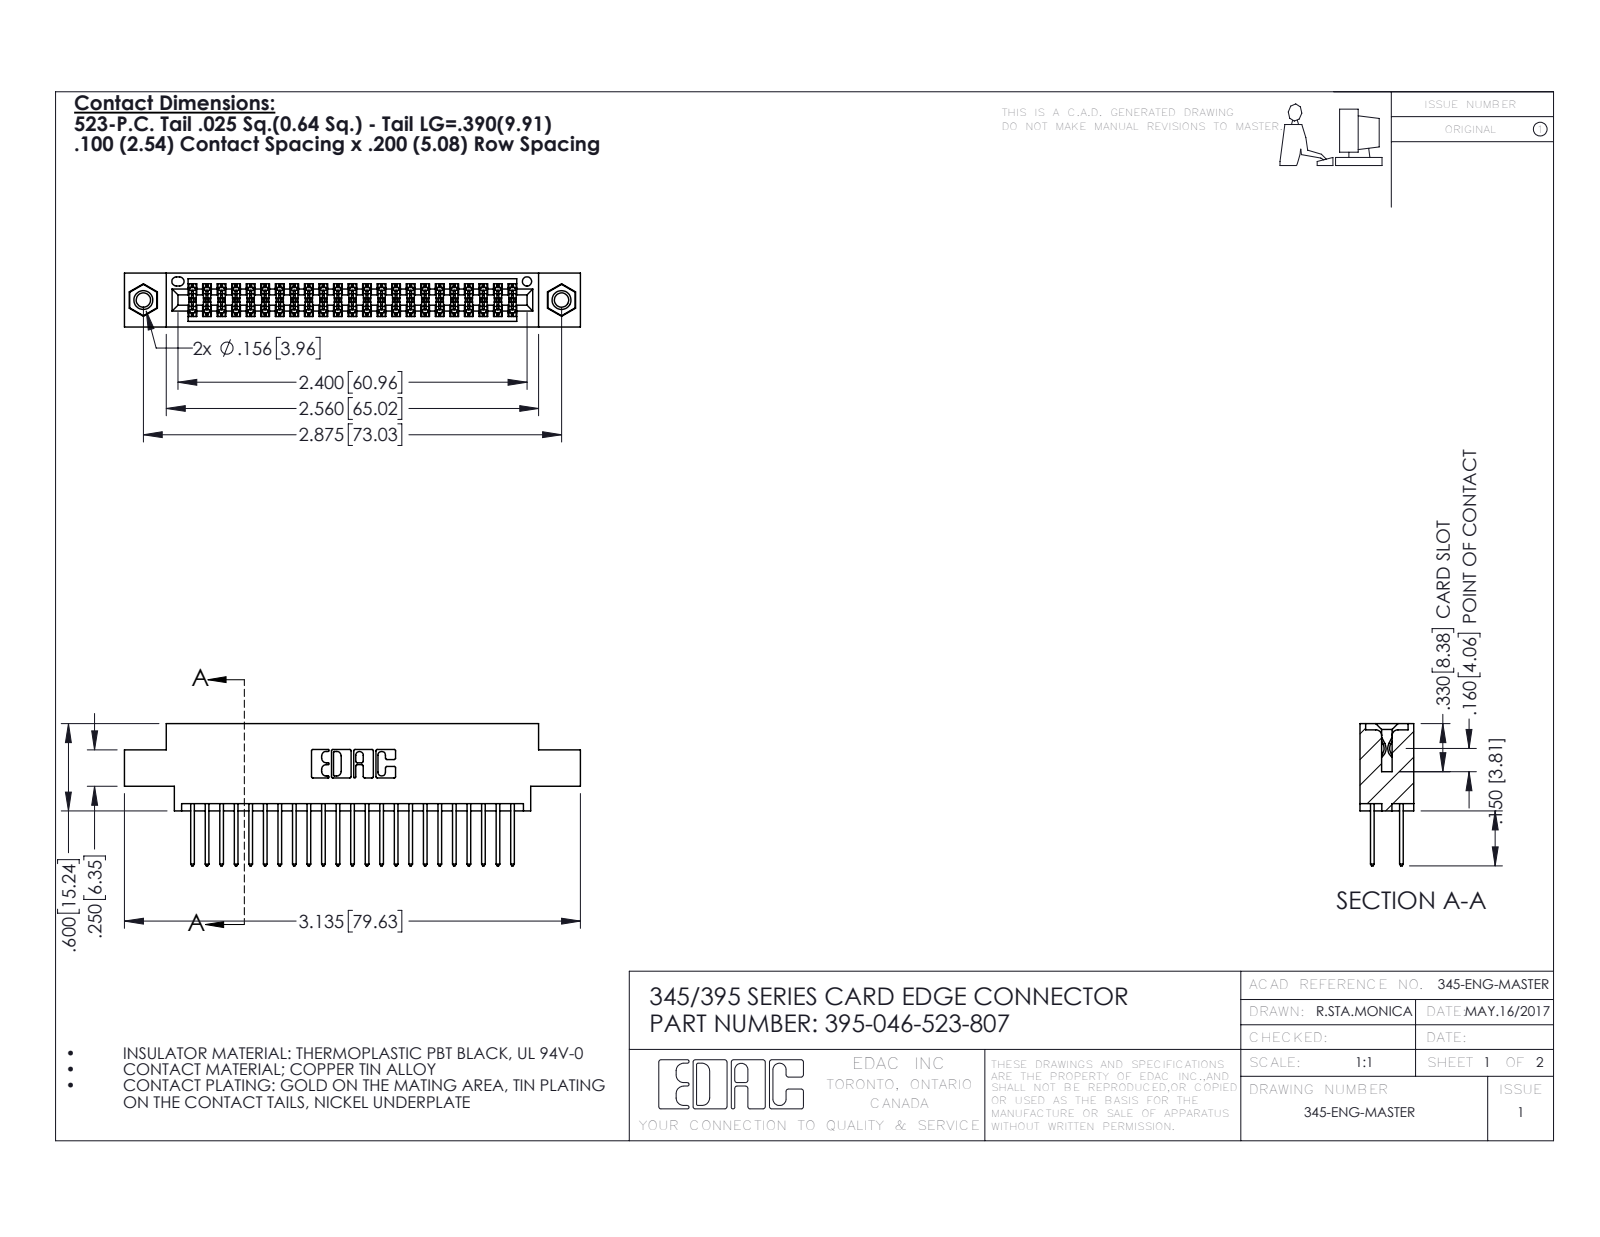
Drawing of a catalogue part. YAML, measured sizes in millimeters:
part_name: "345 Part_0.170 Offset - 0.156 Dia-TI; 395-046-523-807; 345-292-001_345-293-123; 345-250-001_345-250-005-103"
step_written_by: "SolidWorks 2016 (CONFIG_CONTROL_DESIGN)"
units: millimeters
bodies: {solids: 49, faces: 2490, planar: 1634, cylindrical: 840, other: 16}
overall_size: [79.6, 24.8, 9.4]
volume: 7520
surface_area: 11350
round_holes:
  - {diameter: 2.5, count: 2}
  - {diameter: 3.2, count: 2}
  - {diameter: 4, count: 2}
  - {diameter: 1.6, count: 1}
round_bosses_or_shafts:
  - {diameter: 3.9, count: 2}
partial_cylinders:
  - {radius: 0.2, count: 69}
  - {radius: 0.3, count: 46}
  - {radius: 0.3, count: 22}
  - {radius: 0.2, count: 6}
  - {radius: 0.8, count: 6}
  - {radius: 0.7, count: 3}
  - {radius: 0.4, count: 2}
  - {radius: 0.5, count: 2}
face_to_face_distances: [1.8, 7.6, 5.1, 2.5, 6.9, 0.6, 9.4, 5.7, 4.4, 3.8]
hole_center_spacings: [6.9, 67.1, 73]
